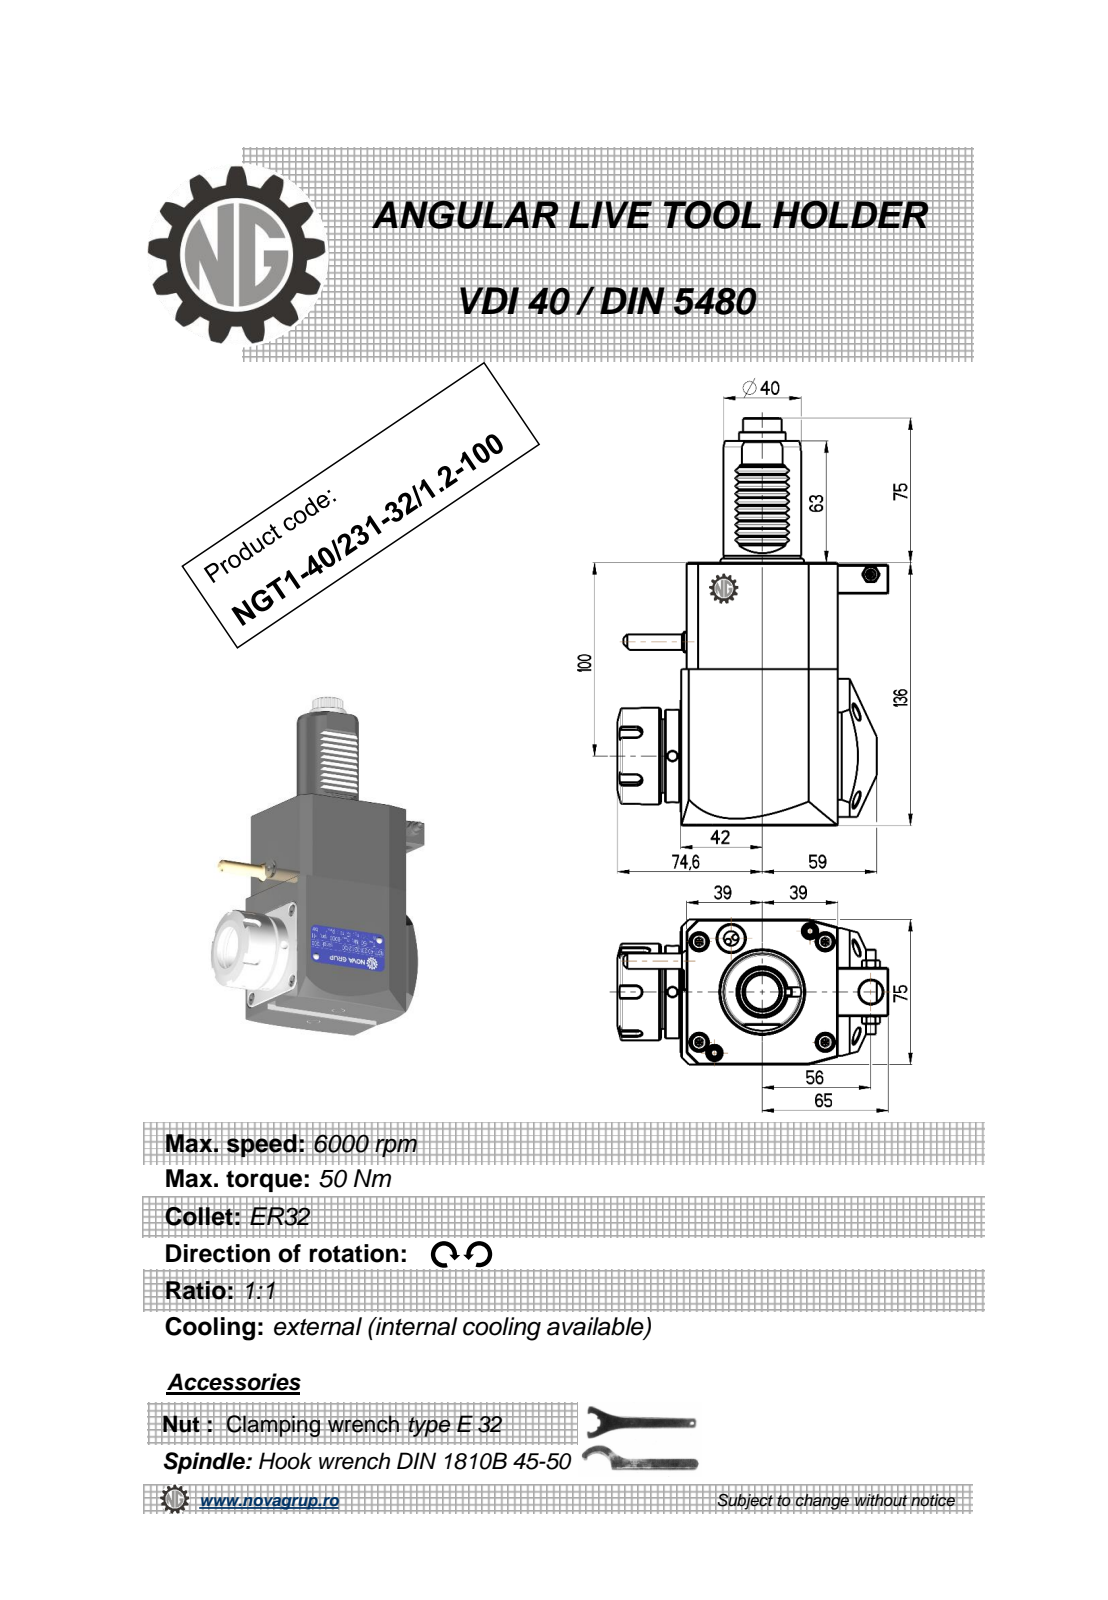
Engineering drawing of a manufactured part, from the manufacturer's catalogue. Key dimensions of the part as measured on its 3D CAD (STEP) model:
Part name (STEP PRODUCT): NGT1_40_231_32_1_2_100
STEP written by: PRO/ENGINEER BY PARAMETRIC TECHNOLOGY CORPORATION, 2010280 (CONFIG_CONTROL_DESIGN)
Units: millimetres
Bodies: 1 solid, 531 faces (193 planar, 185 cylindrical, 153 other)
Overall size (bounding box): 211 × 139.6 × 76.6
Volume: 996 592 mm³ · Surface area: 76 262 mm²
Round holes (diameter × count): ⌀5 ×3, ⌀3 ×1, ⌀4.2 ×1, ⌀9.5 ×1, ⌀12 ×1, ⌀27 ×1
Round bosses / shafts (diameter × count): ⌀50 ×1, ⌀48 ×1, ⌀41 ×1, ⌀40 ×1, ⌀24 ×1, ⌀11.2 ×1, ⌀8.96 ×1, ⌀8 ×1
Partial cylindrical surfaces — rounded edges, fillets, slot ends (radius × count): R2.08 ×48, R0.26 ×12, R0.3 ×10, R0.22 ×6, R3 ×5, R9.08 ×1, R9.92 ×1, R15 ×1
Main face-to-face distances: 75, 136, 78, 81, 3, 2.8, 80.8, 4.5, 7.5, 0.5
Hole centre spacings: 36.22, 61.13, 91.5, 102.25, 138.89
